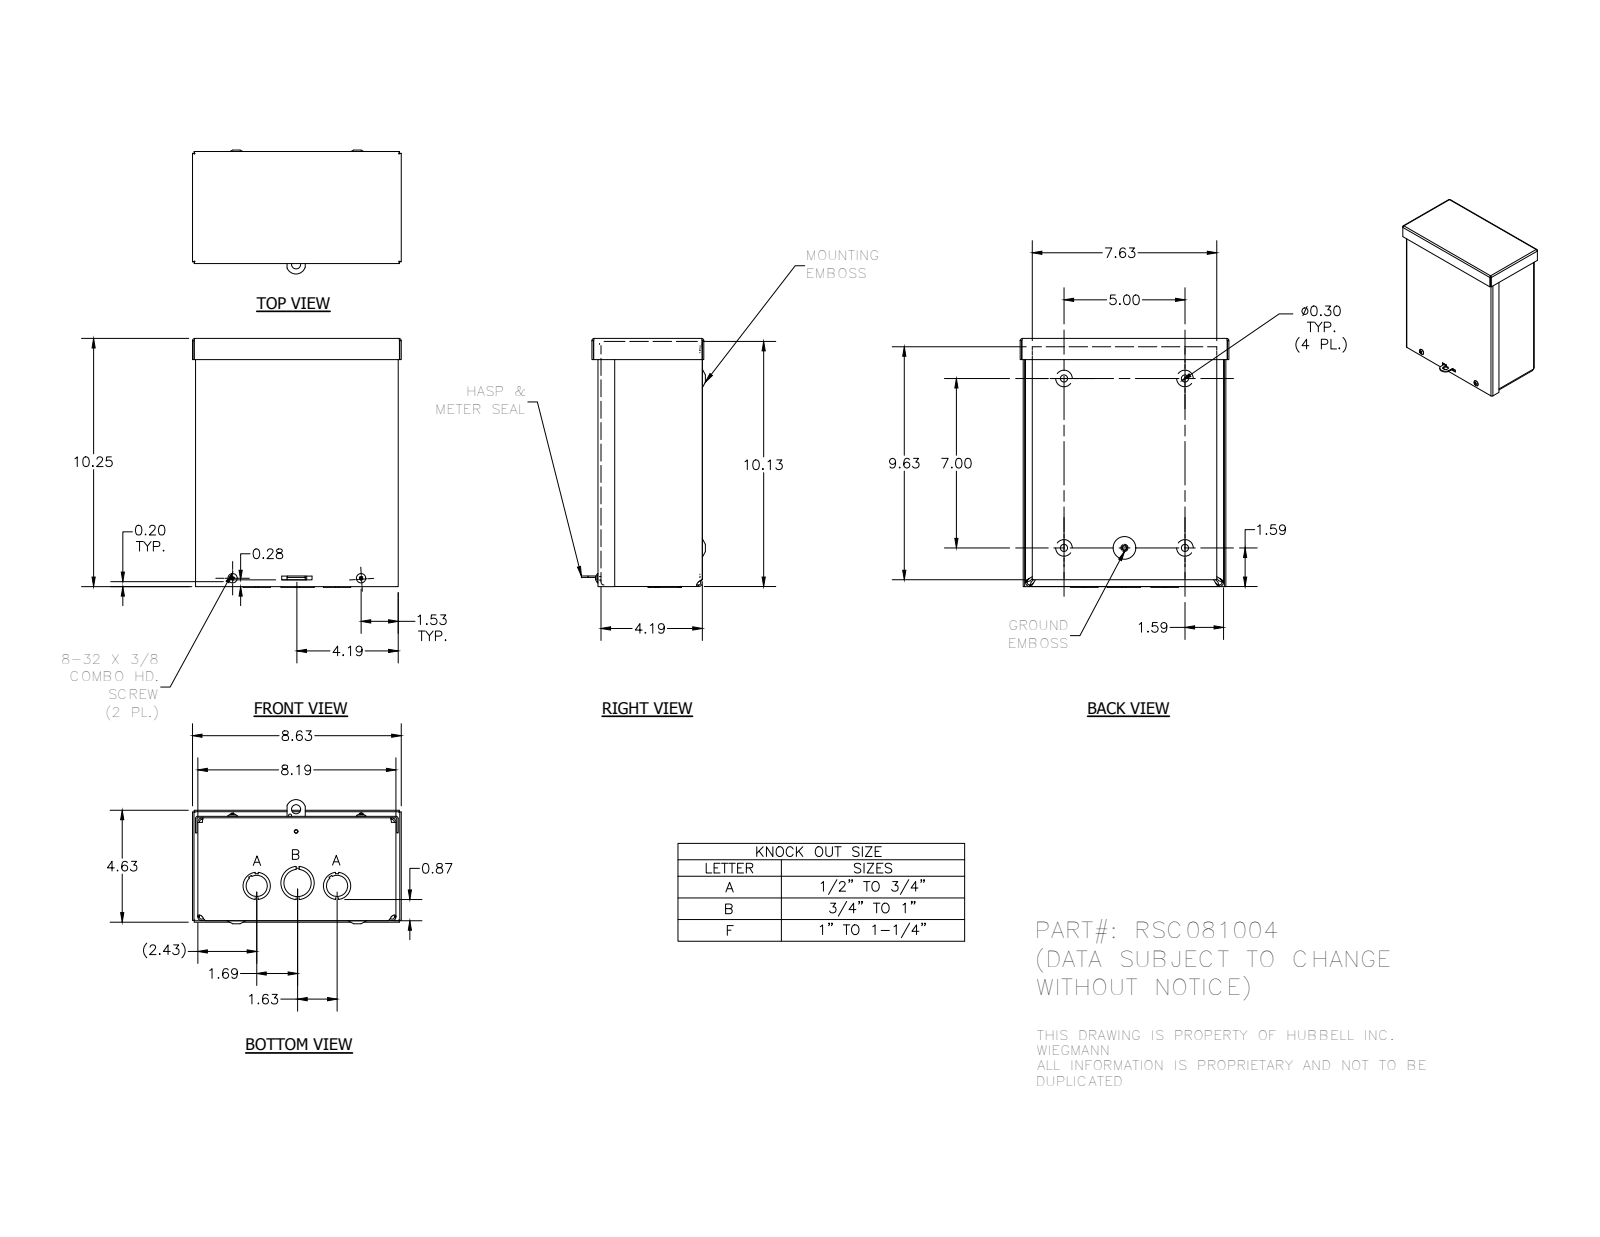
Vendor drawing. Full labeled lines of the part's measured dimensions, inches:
Part name (STEP PRODUCT): RSC081004; RSC081004_WRAP; RSC0810_LID; RSC0804_CAP (+4 more)
STEP written by: Autodesk Inventor 2012 (AUTOMOTIVE_DESIGN)
Units: inches
Bodies: 7 solids, 503 faces (238 planar, 121 cylindrical, 144 other)
Overall size (bounding box): 10.281 × 8.625 × 5.125
Volume: 26.77 in³ · Surface area: 877.9 in²
Round holes (diameter × count): ⌀0.3 ×4, ⌀0.313 ×4, ⌀1.125 ×3, ⌀0.125 ×2, ⌀0.148 ×2, ⌀0.875 ×2, ⌀0.156 ×1, ⌀0.165 ×1, ⌀0.375 ×1, ⌀1.375 ×1
Round bosses / shafts (diameter × count): ⌀0.384 ×2, ⌀0.164 ×2, ⌀0.229 ×1
Partial cylindrical surfaces — rounded edges, fillets, slot ends (radius × count): R0.01 ×10, R0.031 ×8, R0.093 ×8, R0.125 ×8, R0.187 ×8, R0.021 ×4, R0.031 ×4, R0.055 ×4
Main face-to-face distances: 0.062, 0.062, 4.249, 4.187, 8.126, 0.063, 4.312, 4.25, 10.126, 0.124
Hole centre spacings: 1.072, 1.261, 2.5, 5, 5.313, 7, 7.433, 8.063
